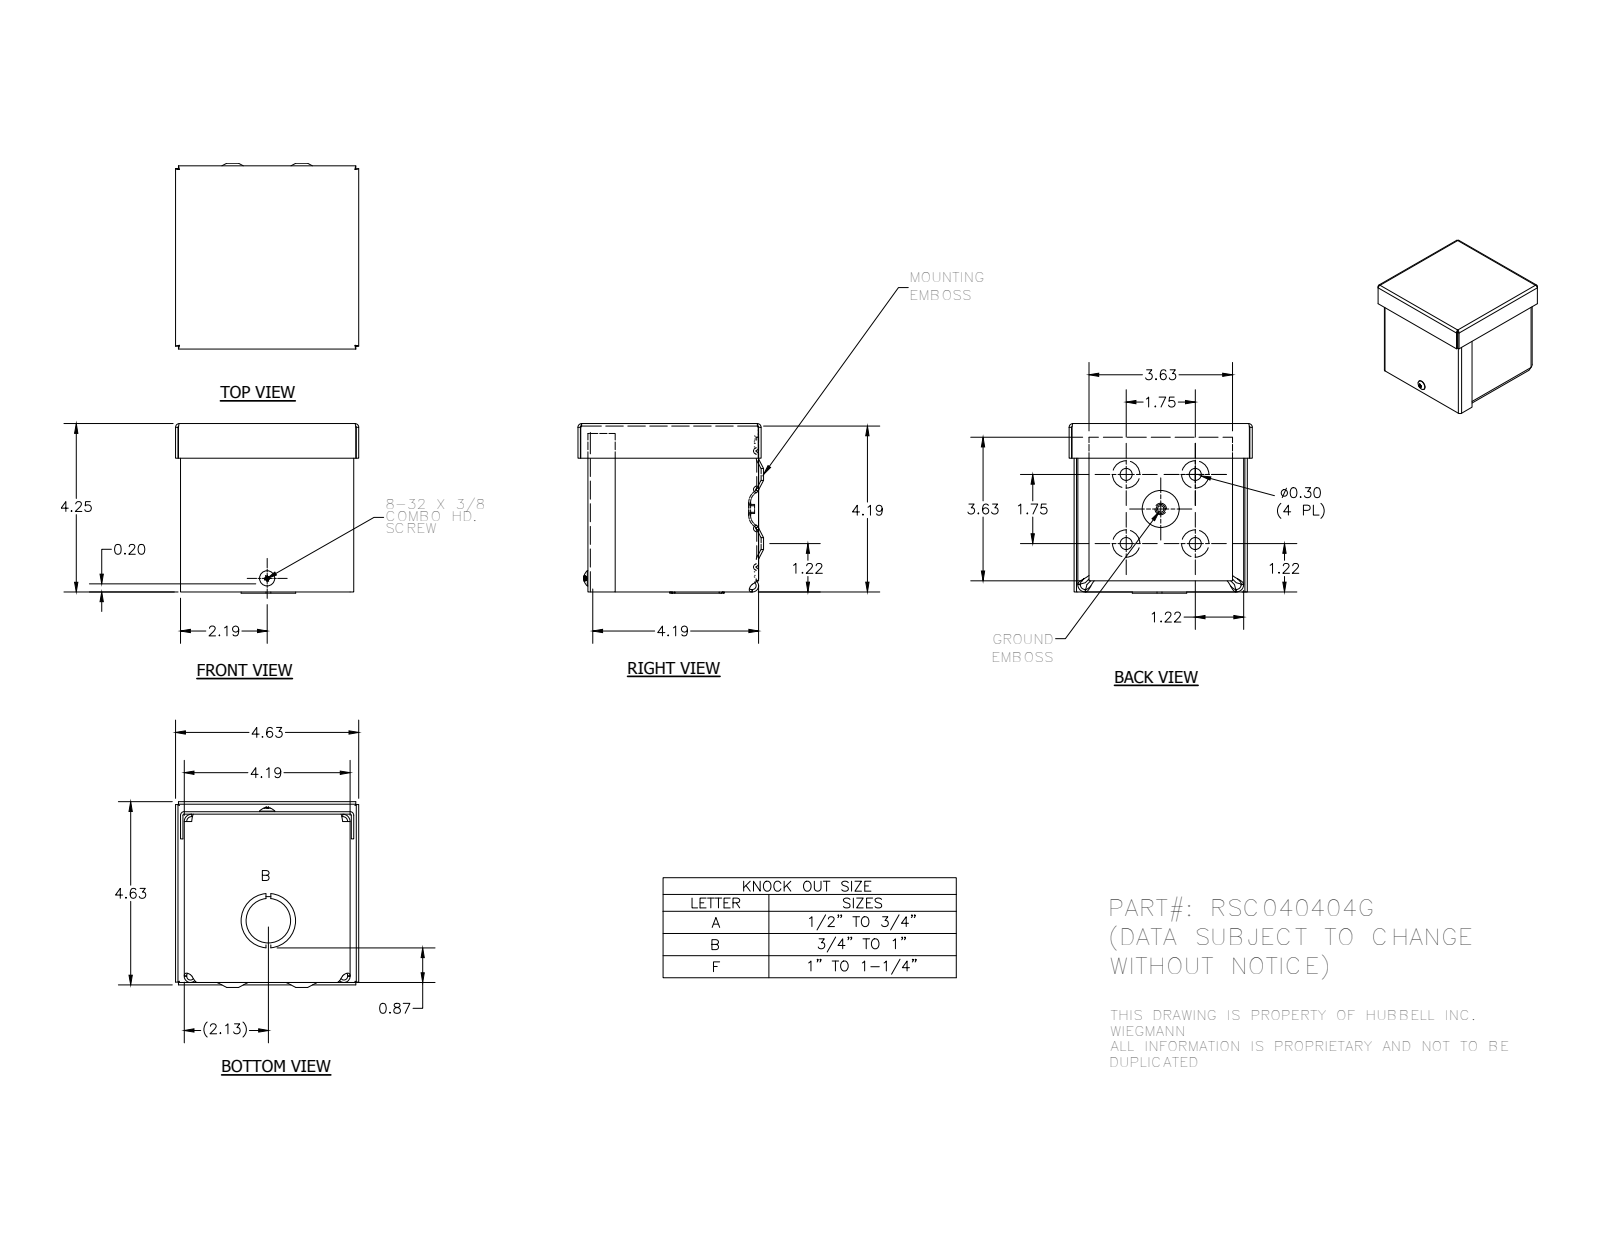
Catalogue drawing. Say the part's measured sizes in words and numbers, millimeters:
The part is named "RSC040404G_WRAP; RSC0404G_LID; RSC0404G_CAP; RSC0404G_BKP (+3 more)". Its 3-D file was written by "Autodesk Inventor 2014 (AUTOMOTIVE_DESIGN)". It is 5 solids with 358 faces: 155 planar, 78 cylindrical and 125 other. Overall it measures 119.09 by 117.47 by 108.72 millimeters. Its volume is 161 202 cubic millimeters and its surface area 209 868 square millimeters. Round holes: 4 of diameter 7.62, 2 of diameter 7.95, 1 of diameter 3.76, 1 of diameter 4.19, 1 of diameter 28.57, 1 of diameter 34.92. Round bosses or shafts: 1 of diameter 9.75, 1 of diameter 5.8, 1 of diameter 4.17. Partial cylindrical surfaces (rounded edges, fillets, slot ends): 8 of radius 3.17, 8 of radius 4.75, 6 of radius 0.79, 6 of radius 2.37, 4 of radius 0.25, 4 of radius 1.4, 4 of radius 1.57, 4 of radius 2.38. The main face-to-face distances are 1.58, 104.79, 1.57, 106.37, 3.15, 107.94, 106.36, 107.93, 103.21, 106.35. The hole center spacings are 31.34, 31.35, 44.32, 44.33, 62.69, 28.21, 28.25, 31.43.
